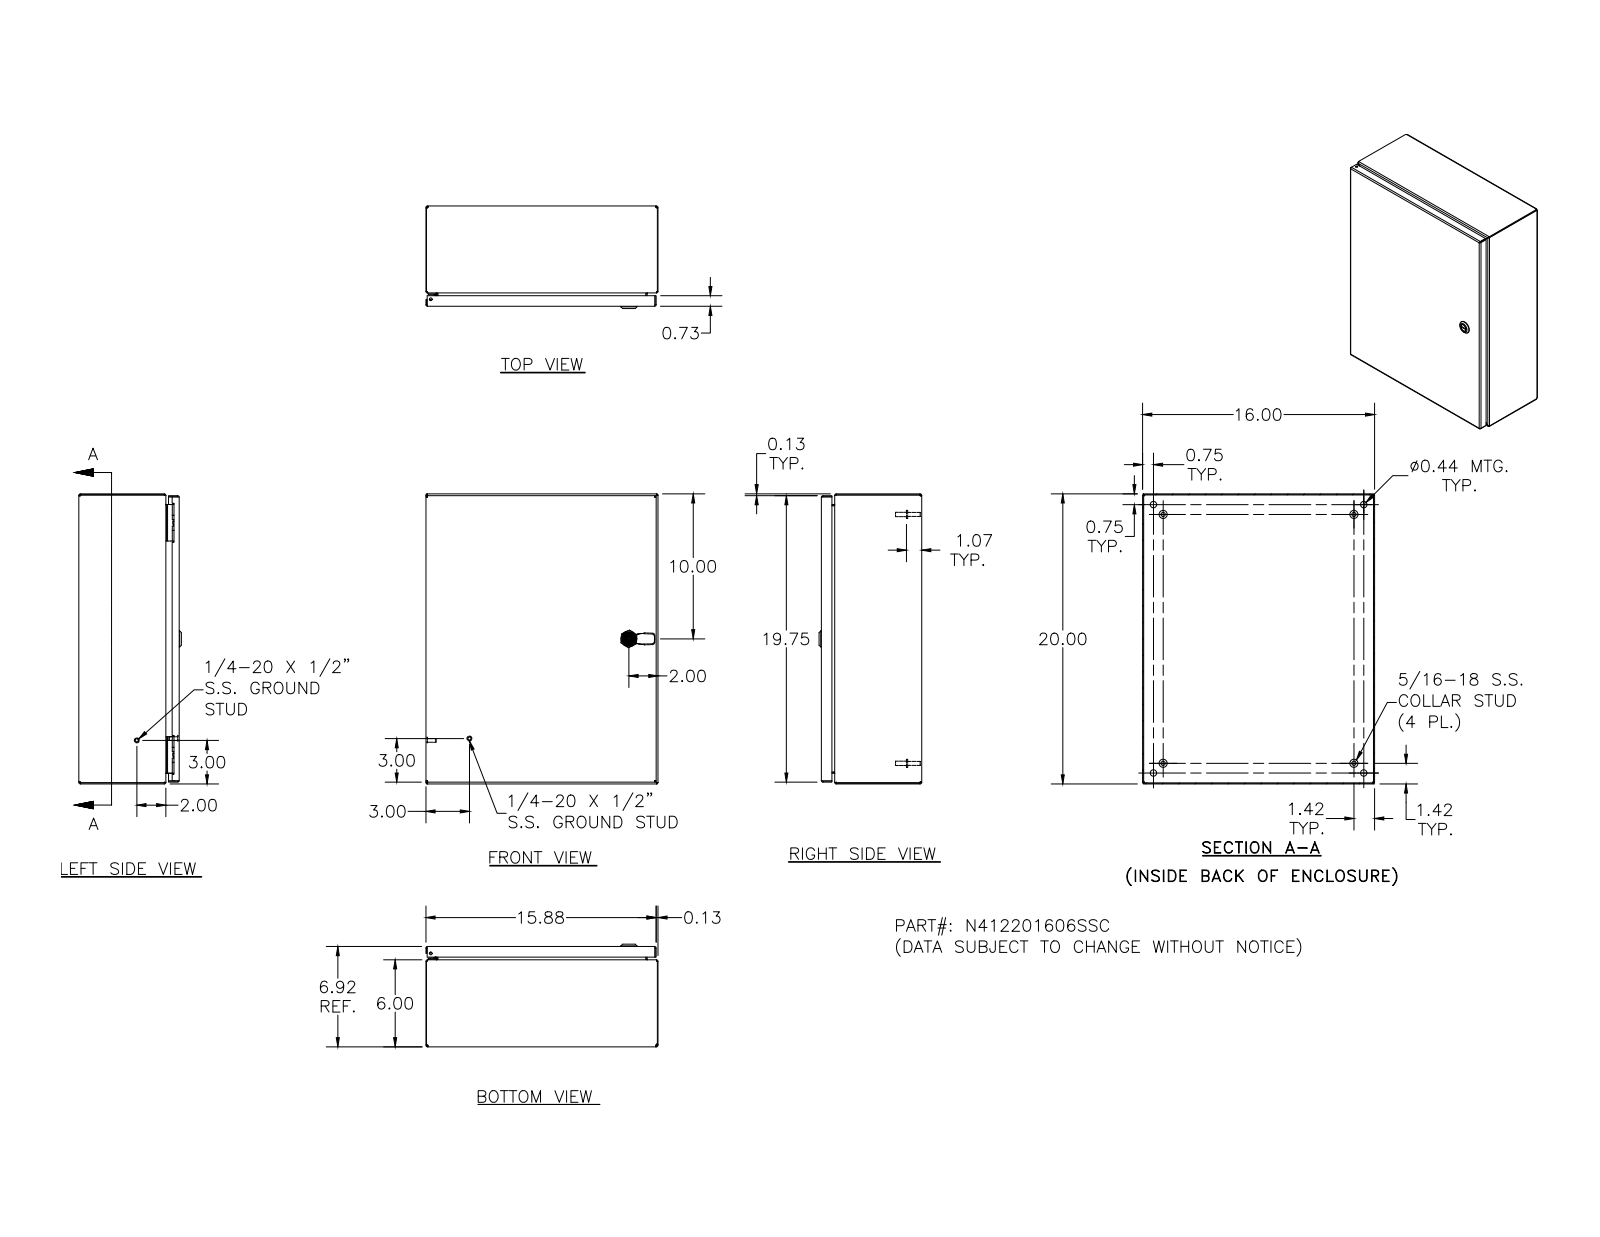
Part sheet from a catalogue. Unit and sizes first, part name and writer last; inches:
Units: inches
Overall size (bounding box): 20 × 16 × 7.075
Round holes (diameter × count): ⌀0.188 ×5, ⌀0.093 ×4, ⌀0.152 ×4, ⌀0.167 ×4, ⌀0.172 ×4, ⌀0.437 ×4, ⌀0.156 ×2, ⌀0.187 ×1, ⌀0.197 ×1, ⌀0.315 ×1, ⌀0.394 ×1, ⌀0.402 ×1
Round bosses / shafts (diameter × count): ⌀0.25 ×10, ⌀0.563 ×4, ⌀0.36 ×4, ⌀0.32 ×4, ⌀0.3 ×4, ⌀0.275 ×4, ⌀0.256 ×4, ⌀0.164 ×4
Partial cylindrical surfaces — rounded edges, fillets, slot ends (radius × count): R0.031 ×30, R0.05 ×26, R0.105 ×20, R0.016 ×18, R0.125 ×14, R0.02 ×9, R0.032 ×8, R0.07 ×8
Main face-to-face distances: 0.074, 6.843, 6.769, 6.917, 15.926, 19.926, 16, 15.852, 20, 19.852
Hole centre spacings: 16, 0.017, 0.66, 16.008, 0.019, 0.5, 0.648, 0.652
Volume: 90.4 in³ · Surface area: 2 460 in²
Bodies: 34 solids, 1384 faces (531 planar, 509 cylindrical, 344 other)
Part name (STEP PRODUCT): N412201606SSC; N412201606SSCBKP; 388151; N4122016SSCLID (+8 more)
STEP written by: Autodesk Inventor 2011 (AUTOMOTIVE_DESIGN)
